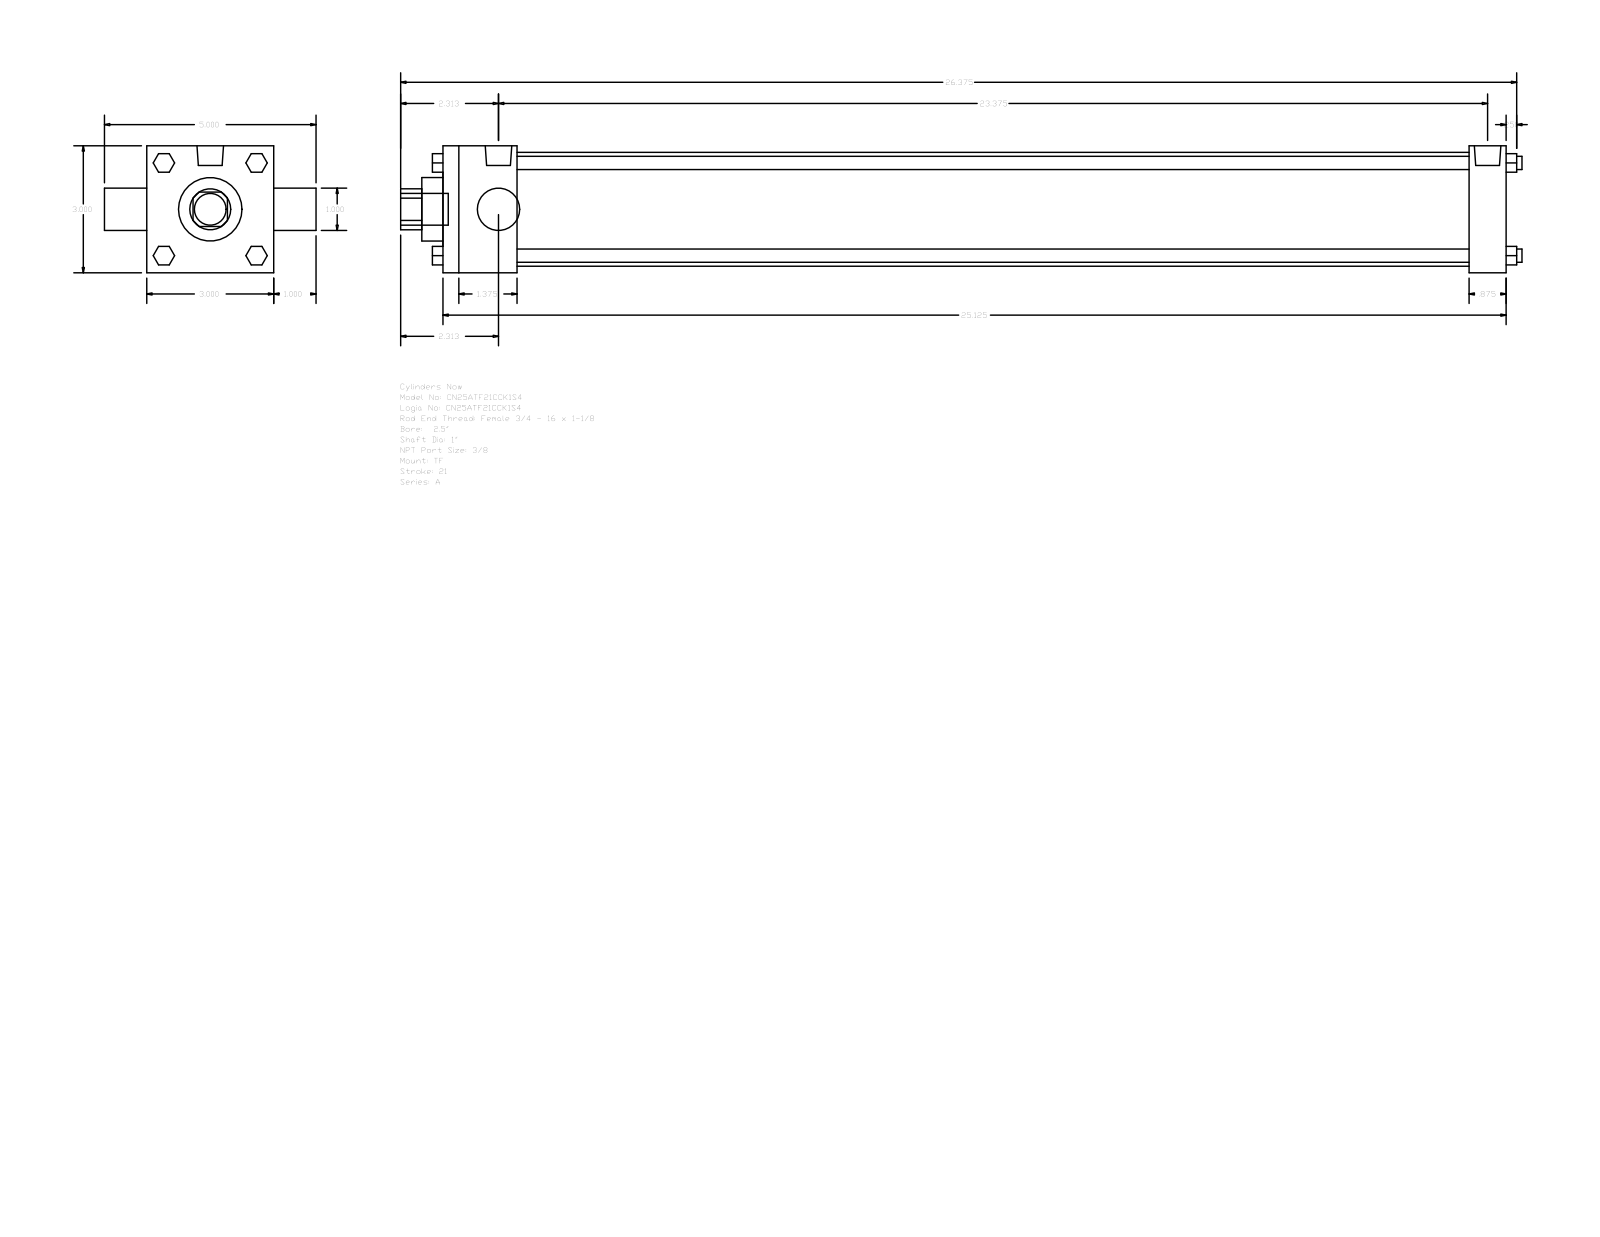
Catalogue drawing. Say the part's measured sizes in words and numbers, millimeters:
The part is named "A_TF__0250_1". Its 3-D file was written by "GSSL Pune (CONFIG_CONTROL_DESIGN)". It is 0 solids with 120 faces: 92 planar, 28 cylindrical and 0 other. Overall it measures 673.1 by 127 by 76.2 millimeters. Round holes: 2 of diameter 25.4, 1 of diameter 38.1, 1 of diameter 68.33. Round bosses or shafts: 4 of diameter 7.94, 3 of diameter 5.56, 2 of diameter 15.93, 1 of diameter 19.05. Partial cylindrical surfaces (rounded edges, fillets, slot ends): 1 of radius 12.29. The main face-to-face distances are 76.2, 638.18, 44.45, 615.95, 571.5, 593.73, 22.23, 25.4, 101.6, 12.7.
